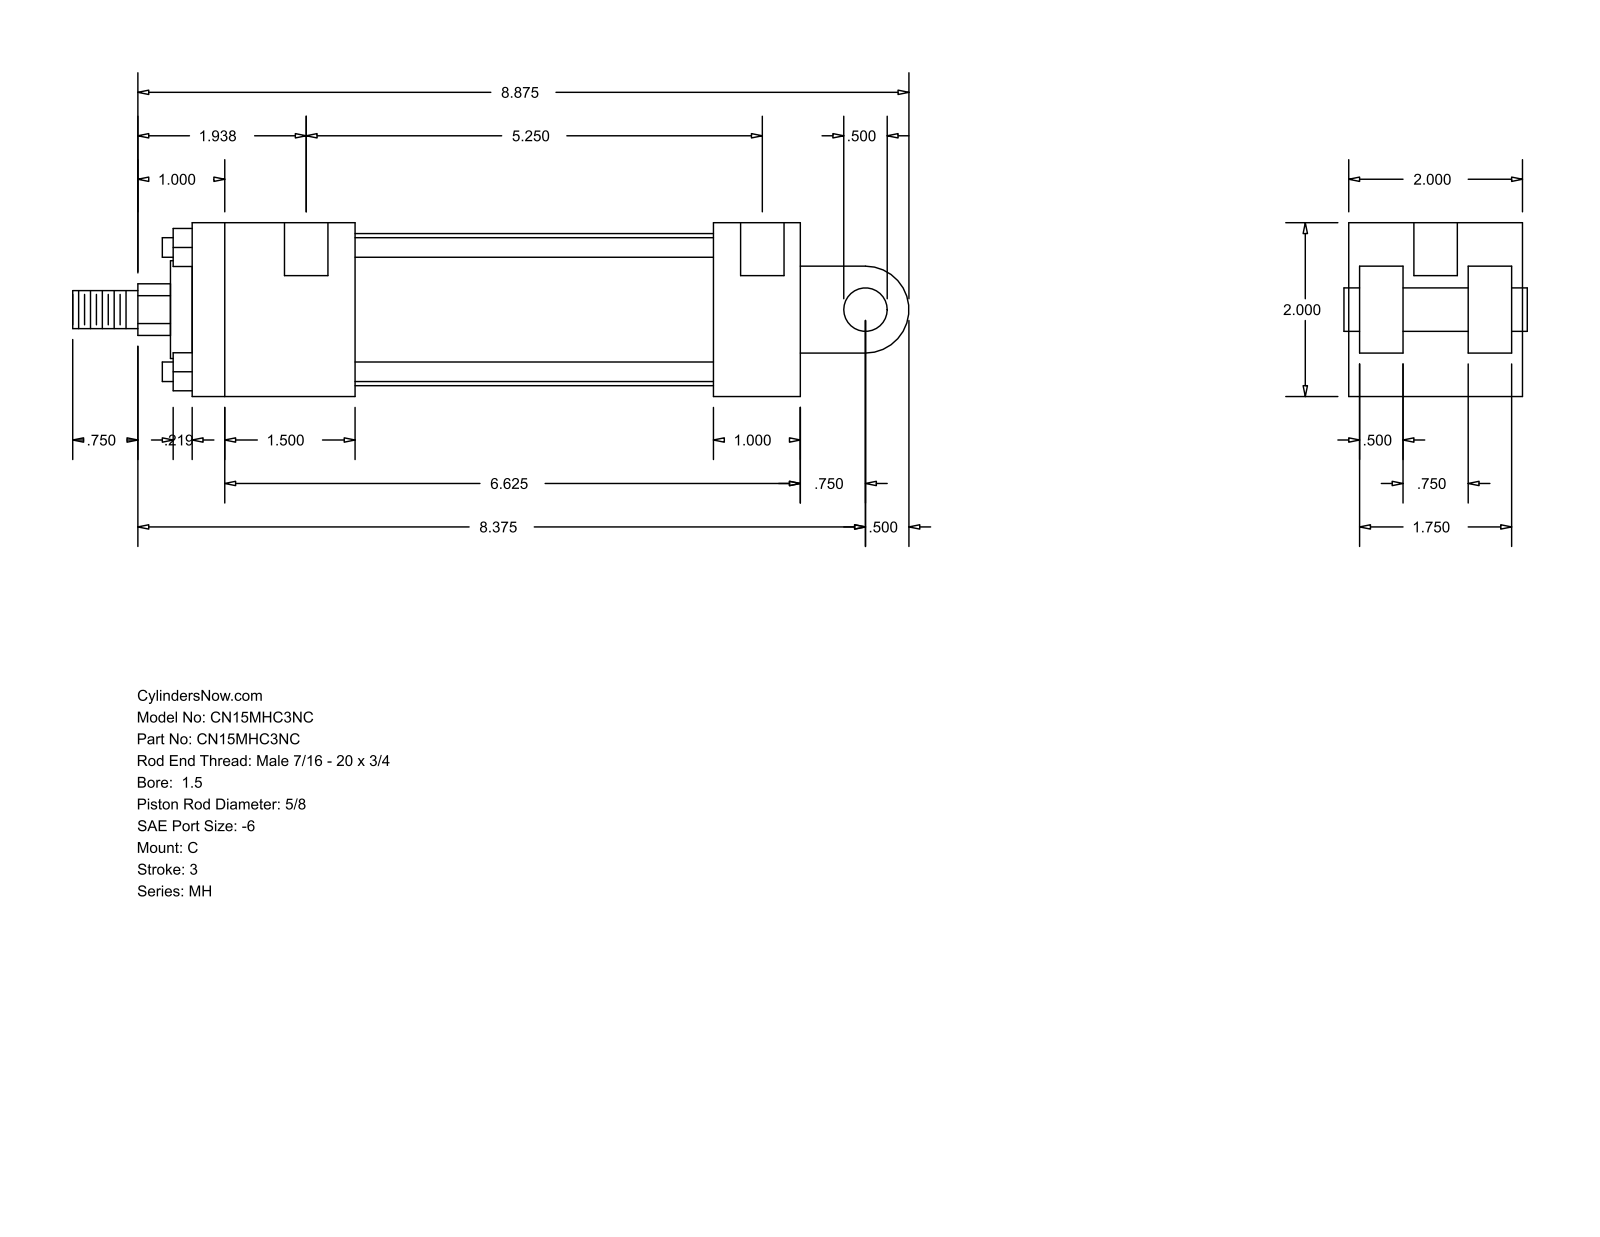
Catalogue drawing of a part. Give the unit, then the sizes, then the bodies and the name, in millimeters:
Units: millimetres
Overall size (bounding box): 244.47 × 50.8 × 50.8
Round holes (diameter × count): ⌀5.56 ×4, ⌀12.7 ×2
Round bosses / shafts (diameter × count): ⌀5.71 ×4, ⌀44.45 ×1, ⌀28.57 ×1, ⌀15.88 ×1, ⌀12.7 ×1, ⌀11.11 ×1
Partial cylindrical surfaces — rounded edges, fillets, slot ends (radius × count): R7.54 ×1, R12.7 ×1
Main face-to-face distances: 50.8, 12.7, 177.8, 25.4, 34.93, 3.17, 47.63, 15.87, 31.76, 38.1
Hole centre spacings: 136.52, 3.17, 133.35
Bodies: 0 solids, 99 faces (70 planar, 29 cylindrical, 0 other)
Part name (STEP PRODUCT): MH_C__0150_0.625
STEP written by: GSSL Pune (CONFIG_CONTROL_DESIGN)
